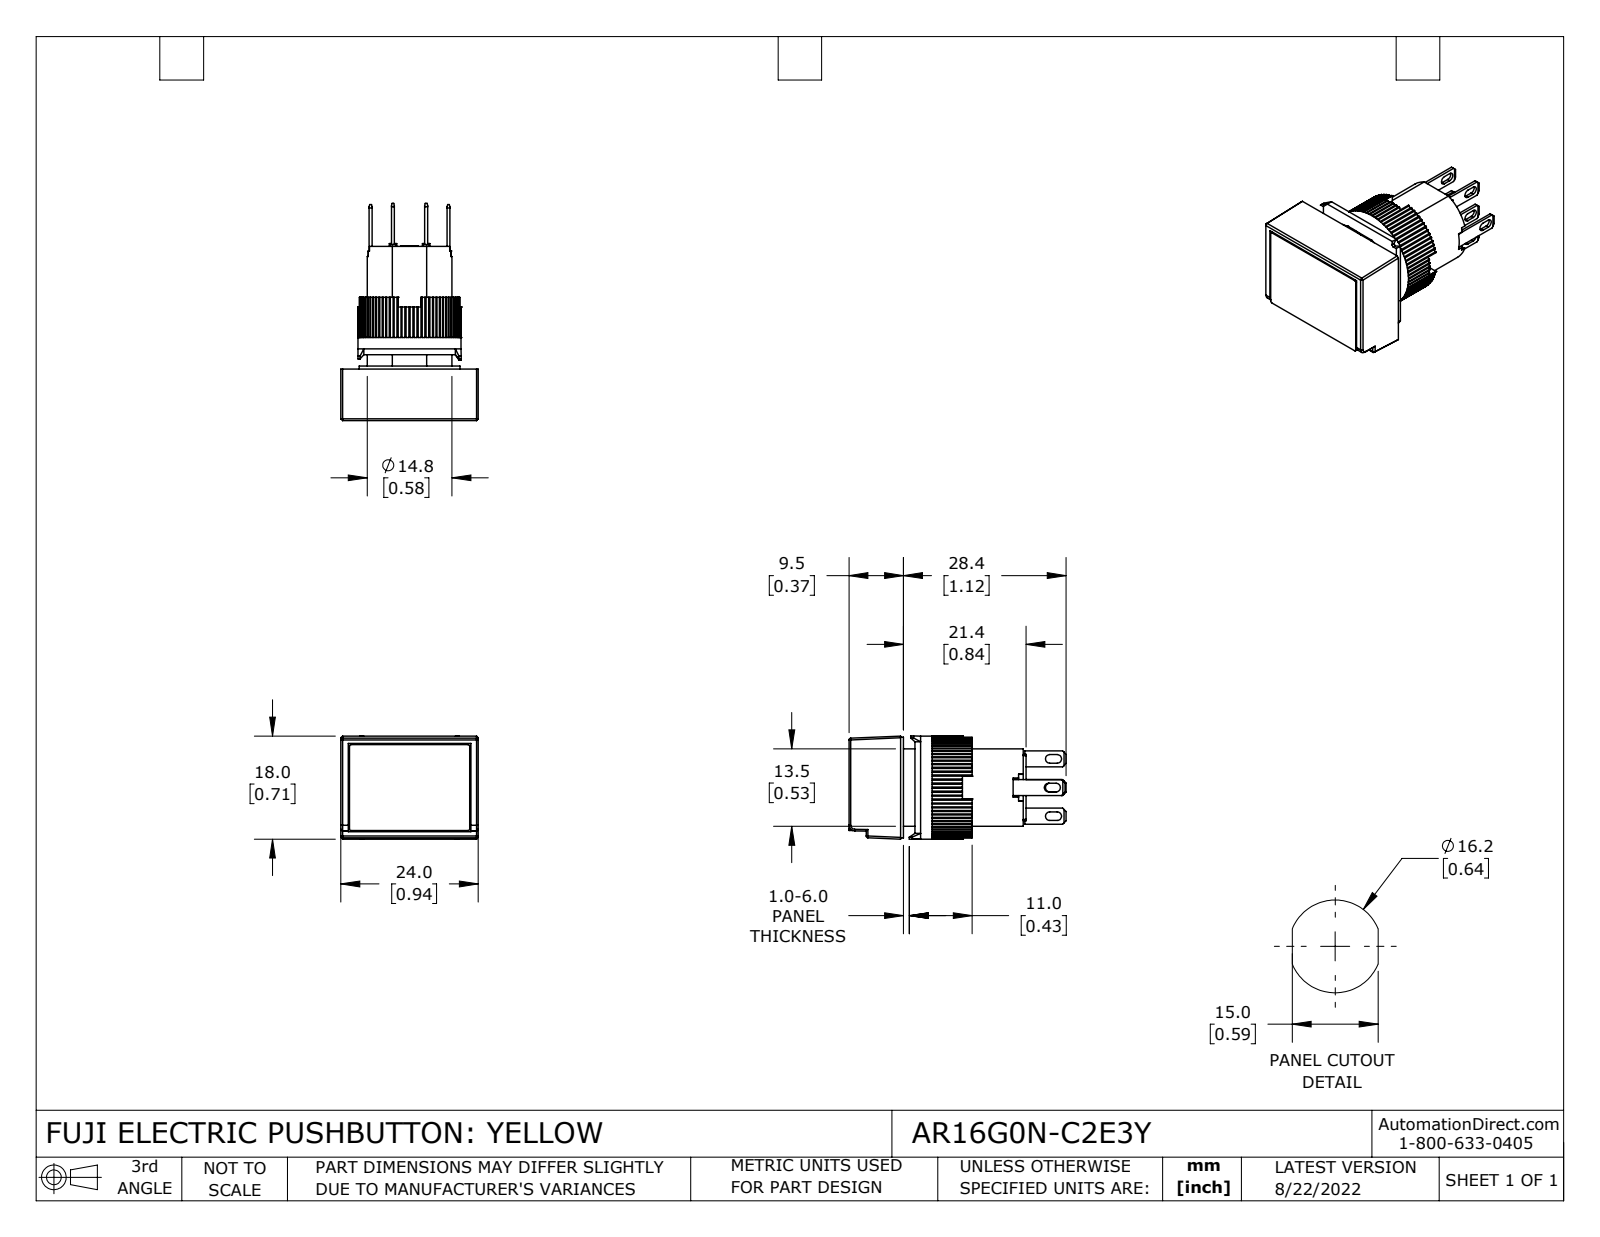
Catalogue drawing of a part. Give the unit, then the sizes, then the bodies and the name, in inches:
Units: inches
Overall size (bounding box): 1.492 × 0.945 × 0.709
Round holes (diameter × count): ⌀0.543 ×1, ⌀0.583 ×1
Round bosses / shafts (diameter × count): ⌀0.709 ×1, ⌀0.693 ×1
Partial cylindrical surfaces — rounded edges, fillets, slot ends (radius × count): R0.01 ×80, R0.008 ×12, R0.03 ×8, R0.012 ×6, R0.039 ×1
Main face-to-face distances: 0.213, 0.354, 0.142, 0.35, 0.492, 0.138, 0.02, 0.843, 0.059, 0.453
Volume: 0.448 in³ · Surface area: 9.503 in²
Bodies: 14 solids, 841 faces (654 planar, 181 cylindrical, 6 other)
Part name (STEP PRODUCT): AR16G0N-C2E3Y
STEP written by: SolidWorks 2021 (CONFIG_CONTROL_DESIGN)
